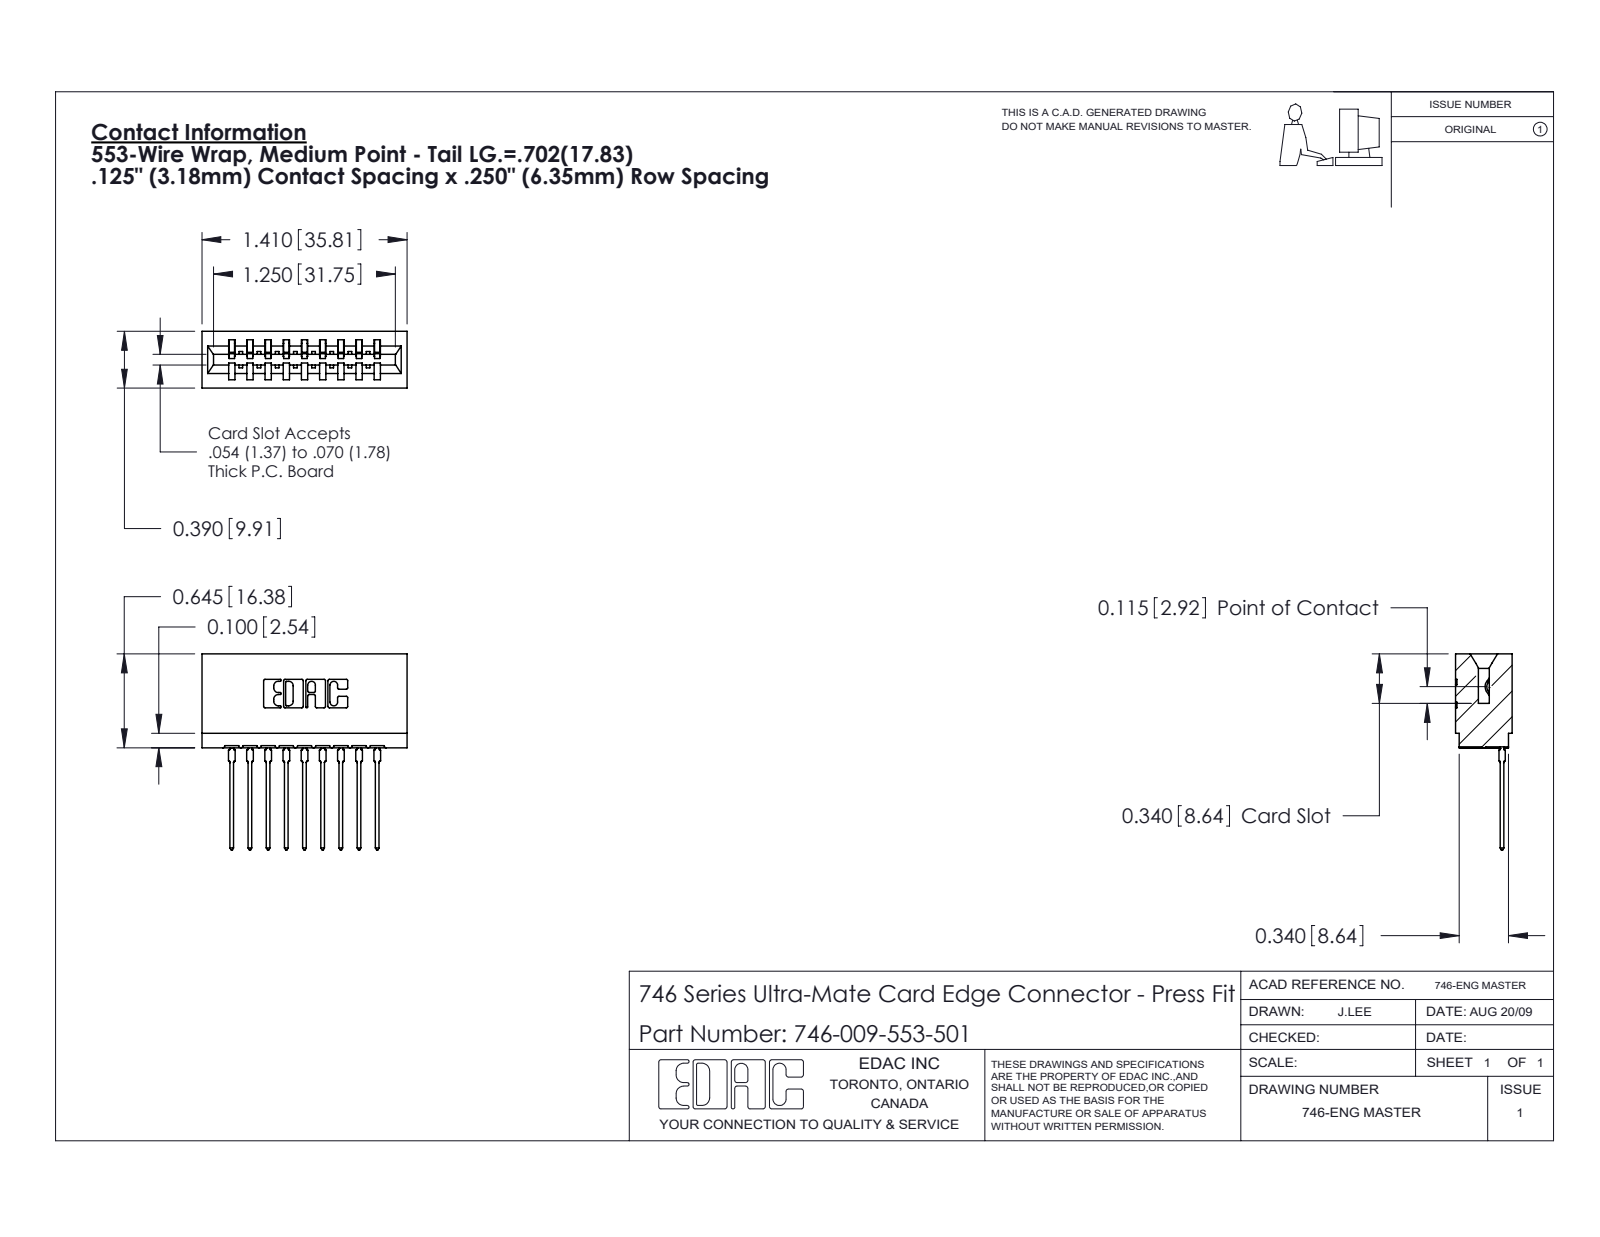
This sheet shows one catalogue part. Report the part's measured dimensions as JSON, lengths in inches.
{"part_name": "746 Part_.340 Slot Depth - 01; 746-292-001_553; 746-009-553-501", "step_written_by": "SolidWorks 2020 (CONFIG_CONTROL_DESIGN)", "units": "inches", "bodies": {"solids": 10, "faces": 1069, "planar": 622, "cylindrical": 213, "other": 234}, "overall_size": [1.41, 1.346, 0.39], "volume_in3": 0.26, "surface_area_in2": 8.381, "partial_cylinders_radius": [[0.01, 22], [0.021, 18], [0.015, 10], [0.007, 6], [0.031, 6], [0.005, 4], [0.011, 4], [0.026, 3]], "face_to_face_distances": [0.25, 0.5, 0.333, 0.042, 0.125, 0.125, 0.057, 0.292, 0.208, 0.083]}
